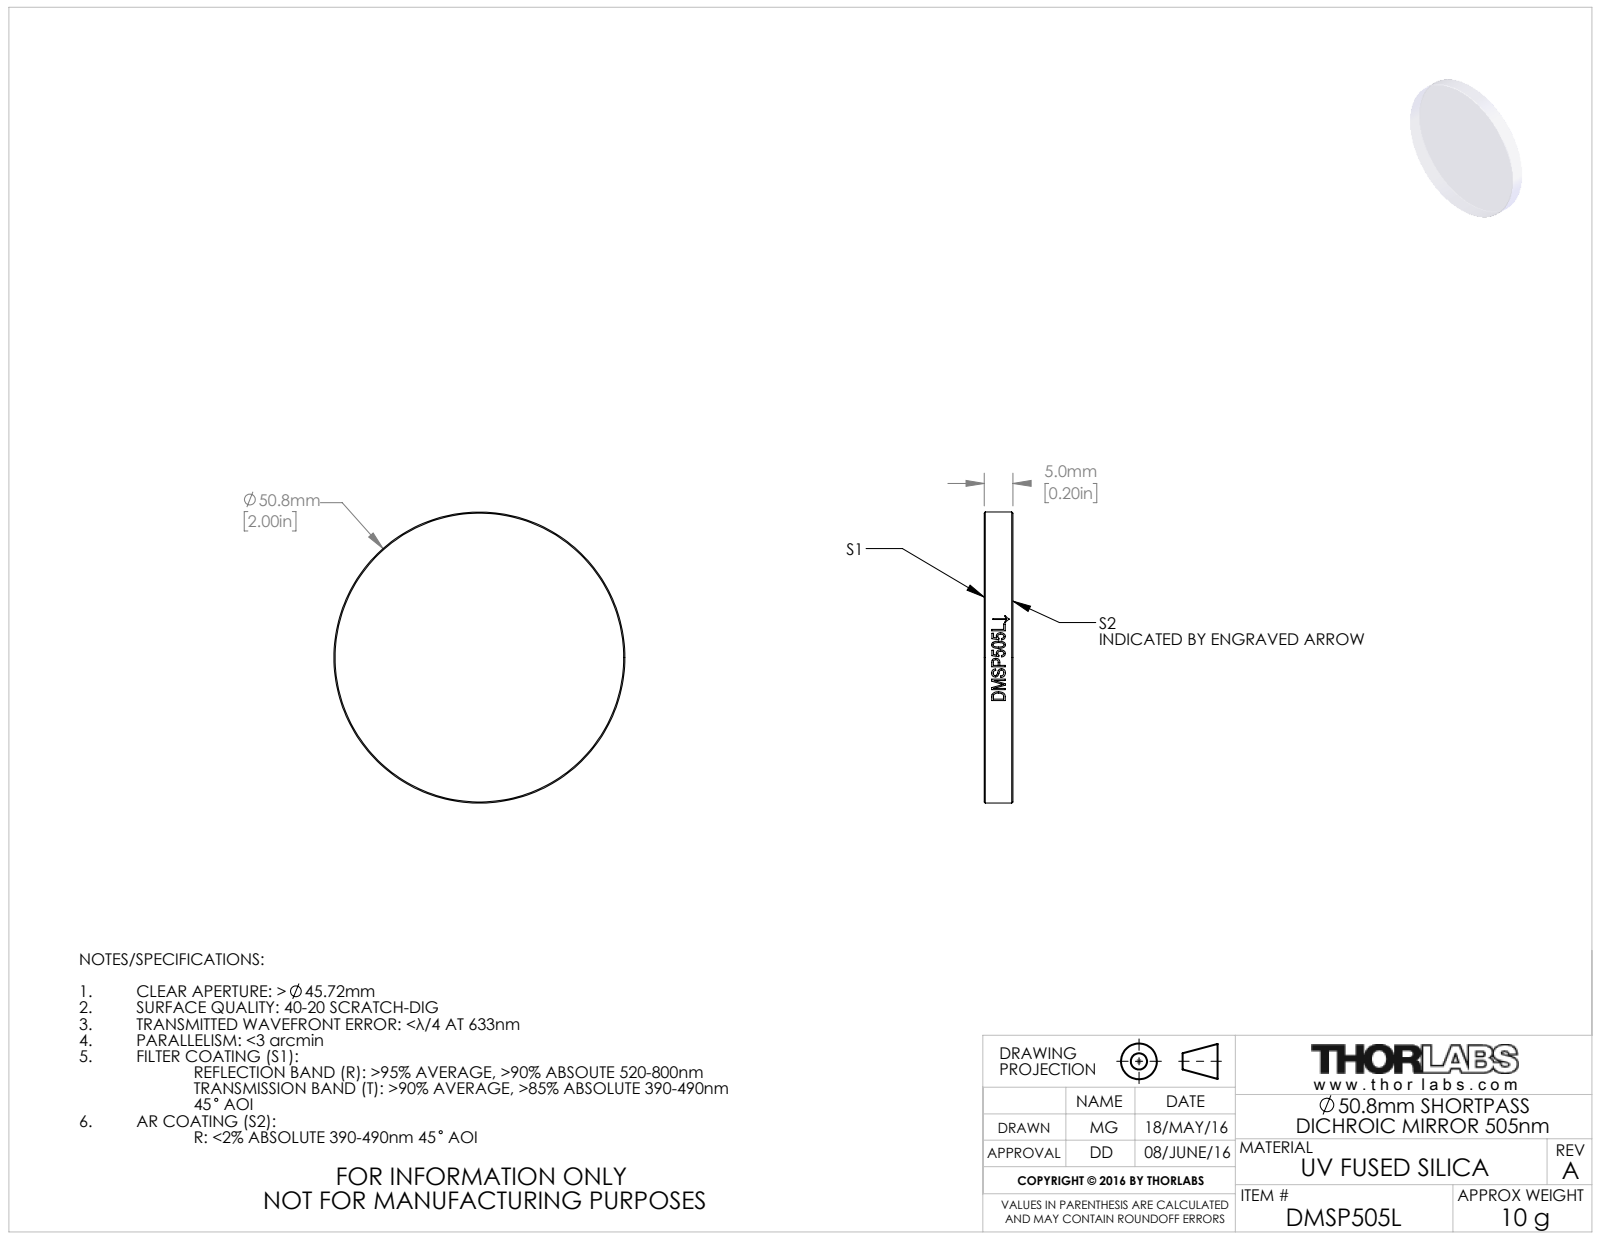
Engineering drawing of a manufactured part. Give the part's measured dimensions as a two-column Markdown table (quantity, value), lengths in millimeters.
| quantity | value |
| --- | --- |
| part name | TTN045164-E0W |
| STEP written by | SolidWorks 2016 (CONFIG_CONTROL_DESIGN) |
| units | millimeters |
| bodies | 1 solid, 20 faces (2 planar, 14 cylindrical, 4 other) |
| overall size | 50.8 × 50.8 × 5 |
| volume | 10 129 mm³ |
| surface area | 4 814 mm² |
| round bosses / shafts (diameter × count) | 50.8 × 1 |
| main face-to-face distances | 5 |
